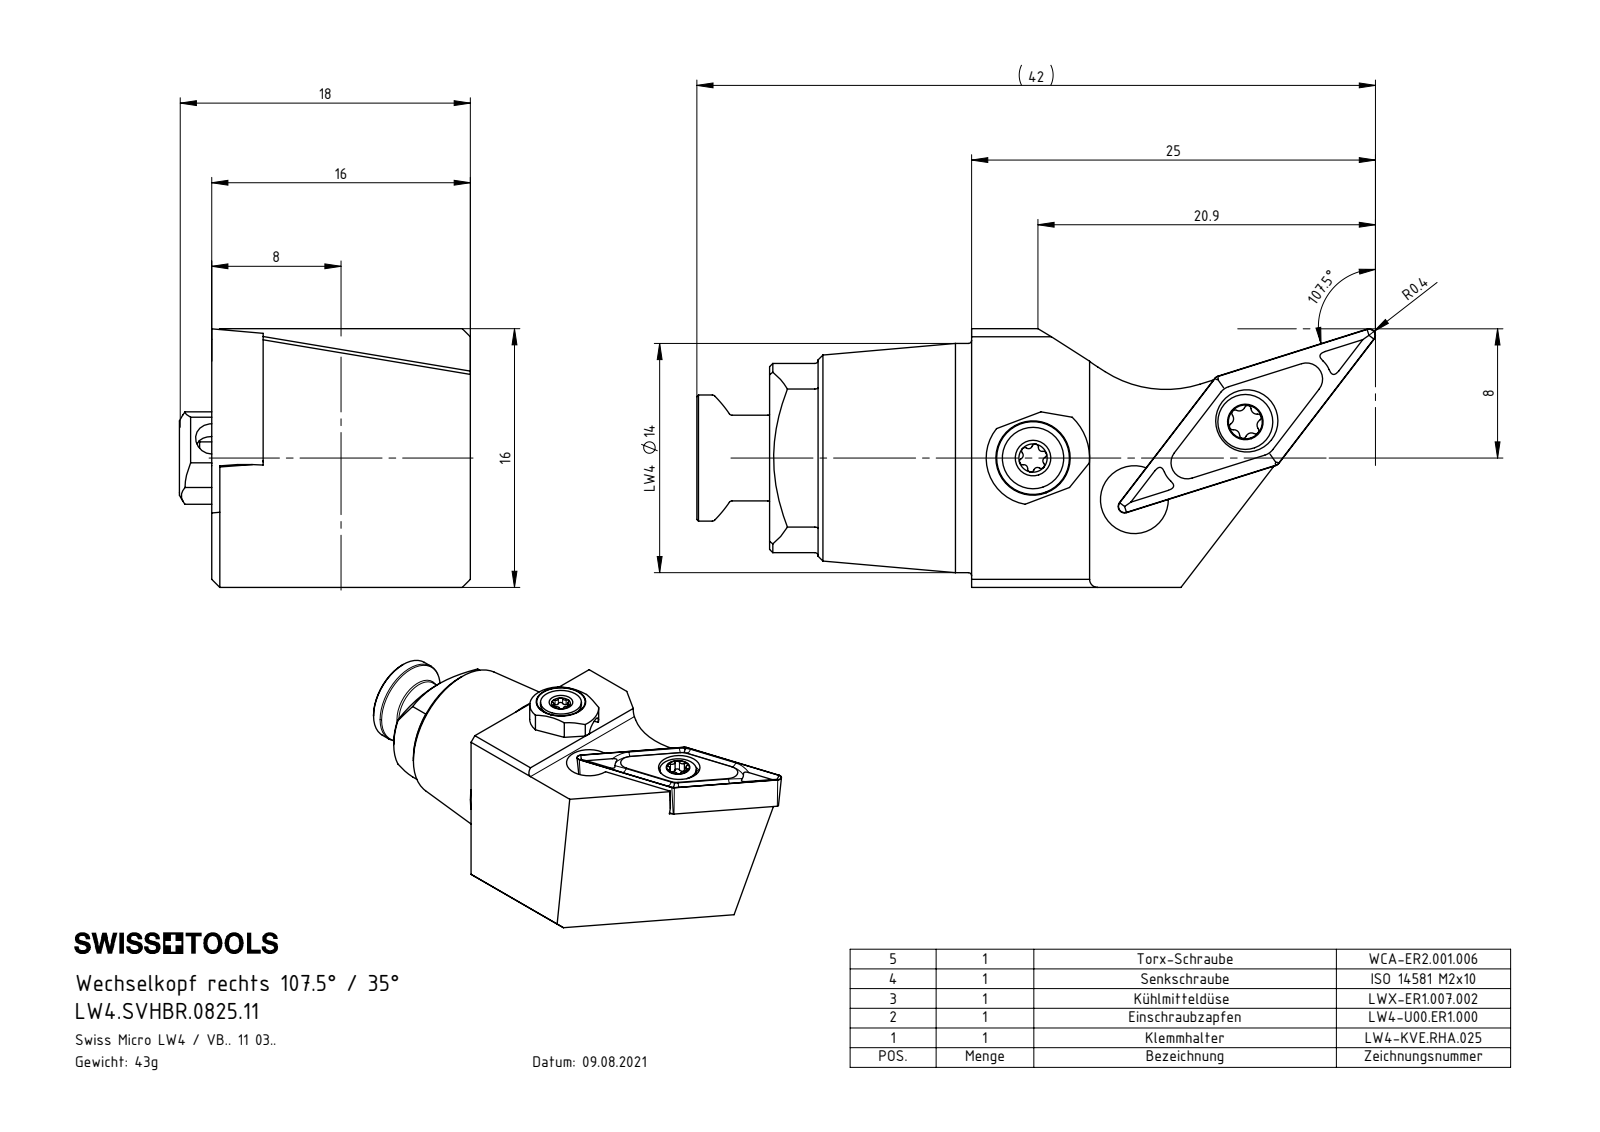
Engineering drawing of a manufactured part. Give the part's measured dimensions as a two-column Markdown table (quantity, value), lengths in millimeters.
| quantity | value |
| --- | --- |
| part name | WCA-ER2.001.006_A; LW4-KVE.RHA.025_A; VBMT110304; ISO 14581 - M2x10 (+1 more) |
| STEP written by | SolidWorks 2022 (CONFIG_CONTROL_DESIGN) |
| units | millimeters |
| bodies | 4 solids, 203 faces (55 planar, 67 cylindrical, 81 other) |
| overall size | 37.49 × 17.95 × 16 |
| volume | 4 984 mm³ |
| surface area | 2 838 mm² |
| round holes (diameter × count) | 2 × 2, 1.6 × 1, 2.05 × 1, 2.8 × 1, 3 × 1, 3.85 × 1, 4.2 × 1, 5.5 × 1 |
| round bosses / shafts (diameter × count) | 14.17 × 1, 3.8 × 1, 3.4 × 1, 2.5 × 1, 2 × 1 |
| partial cylindrical surfaces (radius × count) | 0.2 × 8, 0.21 × 6, 0.24 × 6, 0.36 × 4, 0.36 × 2, 0.5 × 1, 5.85 × 1, 7 × 1 |
| main face-to-face distances | 16, 12.82, 3.18, 15.5, 2.68, 0.5, 12.5, 4, 12, 3 |
| hole center spacings | 6.78, 8.38, 8.49, 13.33, 13.43 |
